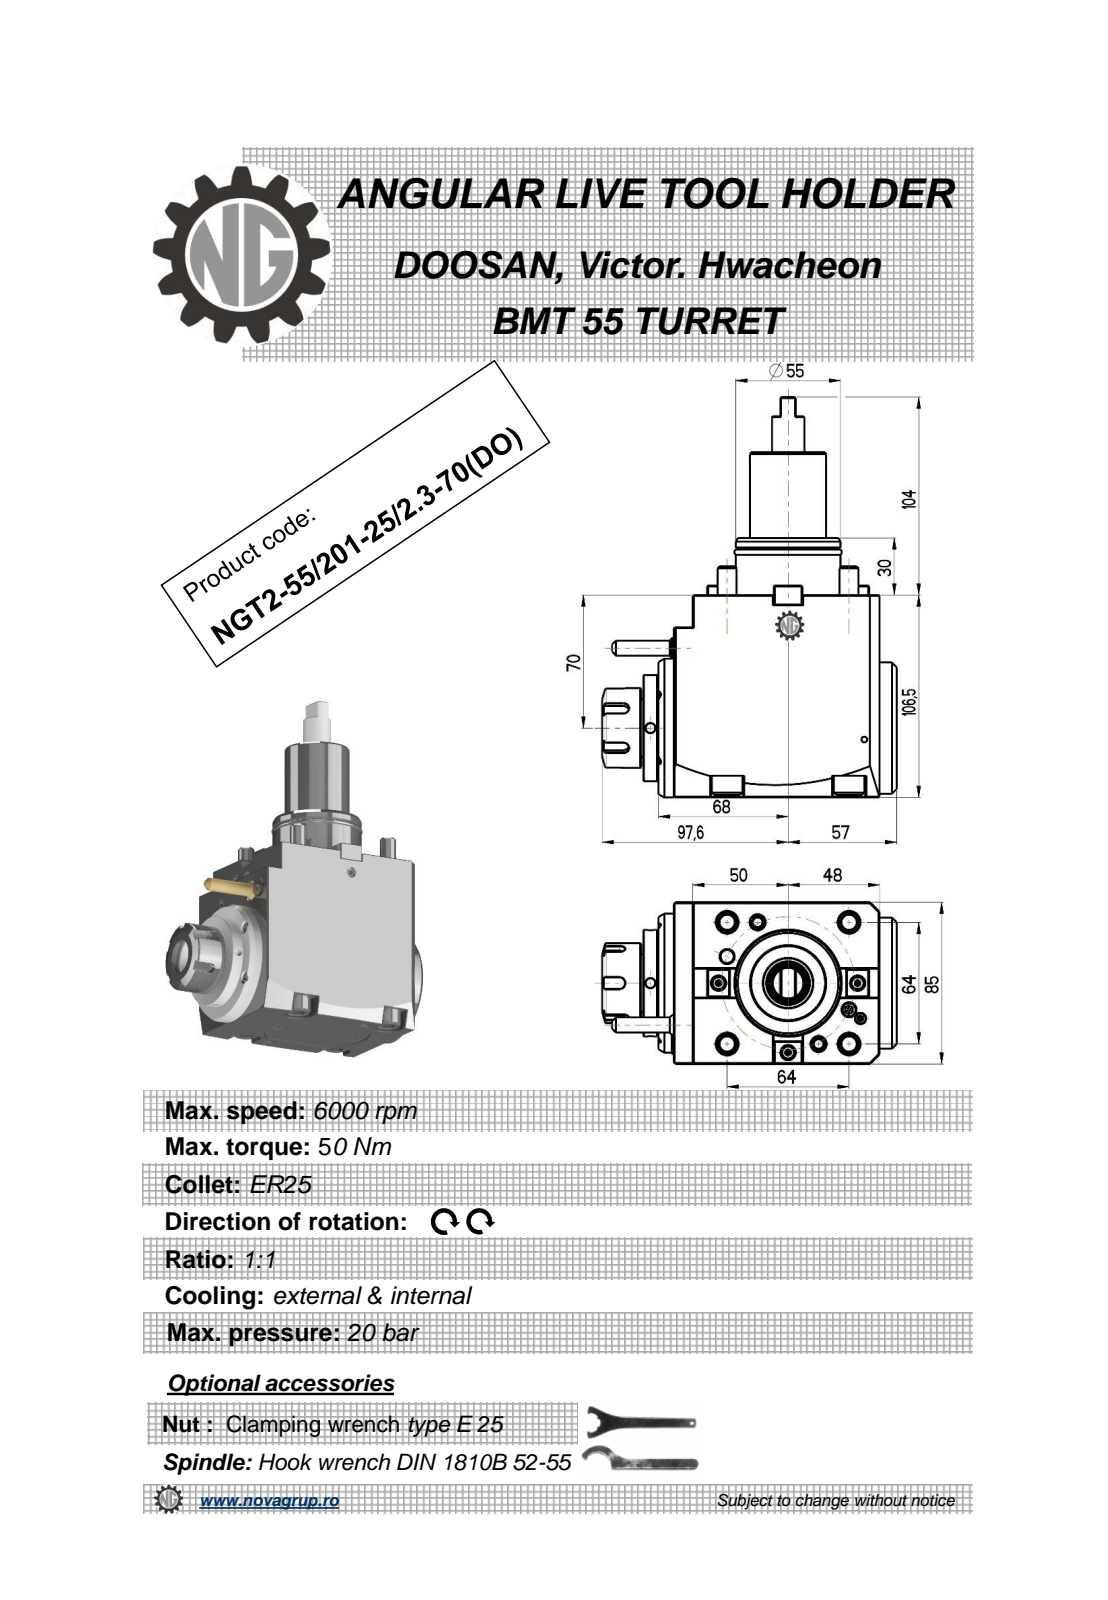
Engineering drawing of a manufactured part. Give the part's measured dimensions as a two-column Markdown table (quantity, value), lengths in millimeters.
| quantity | value |
| --- | --- |
| part name | NGT2_55_201_25_1_3_70_DO |
| STEP written by | PRO/ENGINEER BY PARAMETRIC TECHNOLOGY CORPORATION, 2010280 (CONFIG_CONTROL_DESIGN) |
| units | millimeters |
| bodies | 2 solids, 482 faces (228 planar, 109 cylindrical, 145 other) |
| overall size | 210.5 × 155.9 × 85 |
| volume | 1 194 000 mm³ |
| surface area | 105 808 mm² |
| round holes (diameter × count) | 5 × 3, 6.8 × 2, 3 × 1, 12 × 1 |
| round bosses / shafts (diameter × count) | 16 × 4, 10 × 4, 73 × 1, 68 × 1, 56 × 1, 55 × 1, 50 × 1, 43.4 × 1 |
| partial cylindrical surfaces (radius × count) | 0.32 × 20, 0.22 × 6, 3 × 5, 8.5 × 4, 0.8 × 2, 480 × 2 |
| main face-to-face distances | 85, 106.5, 8, 10.3, 108, 118.3, 116, 126.3, 10, 16 |
| hole center spacings | 42.62, 69.86, 105.19 |
